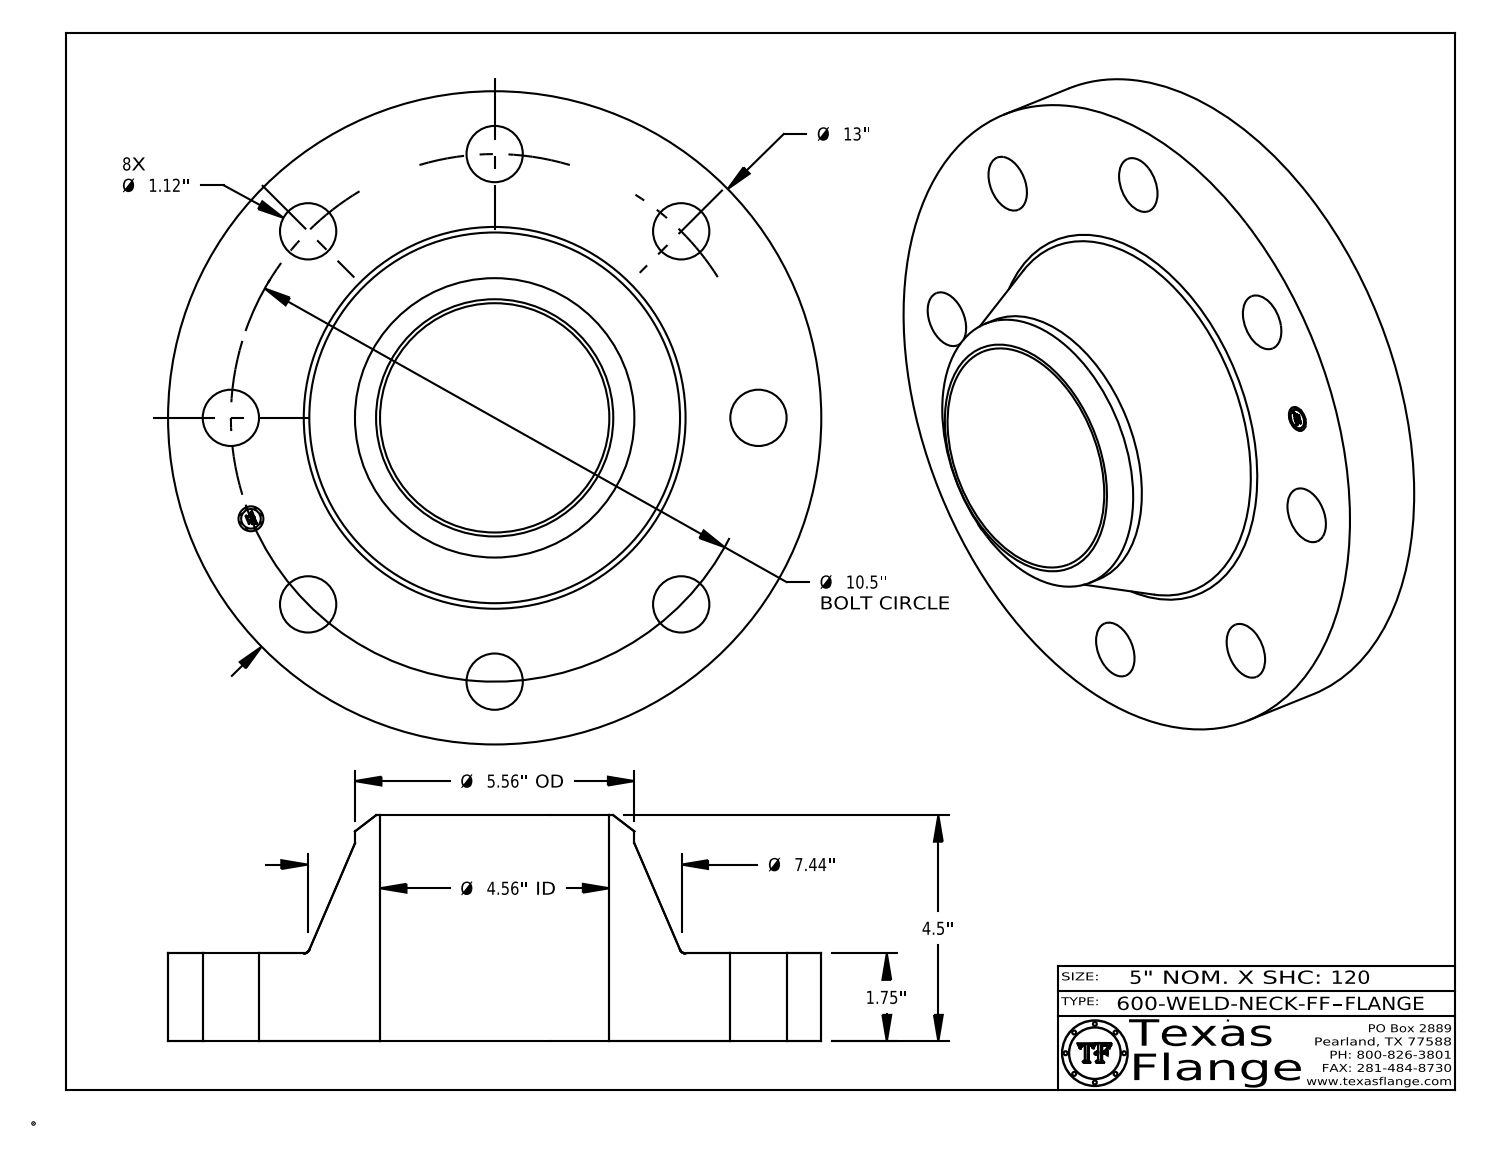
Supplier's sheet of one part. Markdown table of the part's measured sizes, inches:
| quantity | value |
| --- | --- |
| part name | 600-WELD-NECK-FF |
| STEP written by | CATIA V5 STEP AP214 (AUTOMOTIVE_DESIGN) |
| units | inches |
| bodies | 1 solid, 416 faces (368 planar, 42 cylindrical, 6 other) |
| overall size | 13 × 13 × 4.5 |
| volume | 230.6 in³ |
| surface area | 437.3 in² |
| round holes (diameter × count) | 1.12 × 8, 0.495 × 1, 4.563 × 1 |
| round bosses / shafts (diameter × count) | 0.03 × 8, 13 × 1, 5.56 × 1, 0.39 × 1 |
| main face-to-face distances | 1.75, 4.5, 2.75, 1.735, 0.015, 2.765, 0.148, 0.145, 0.027, 0.096 |
| hole center spacings | 5.25, 4.018, 9.701, 7.424, 7.425, 2.048, 5.833, 8.73 |
